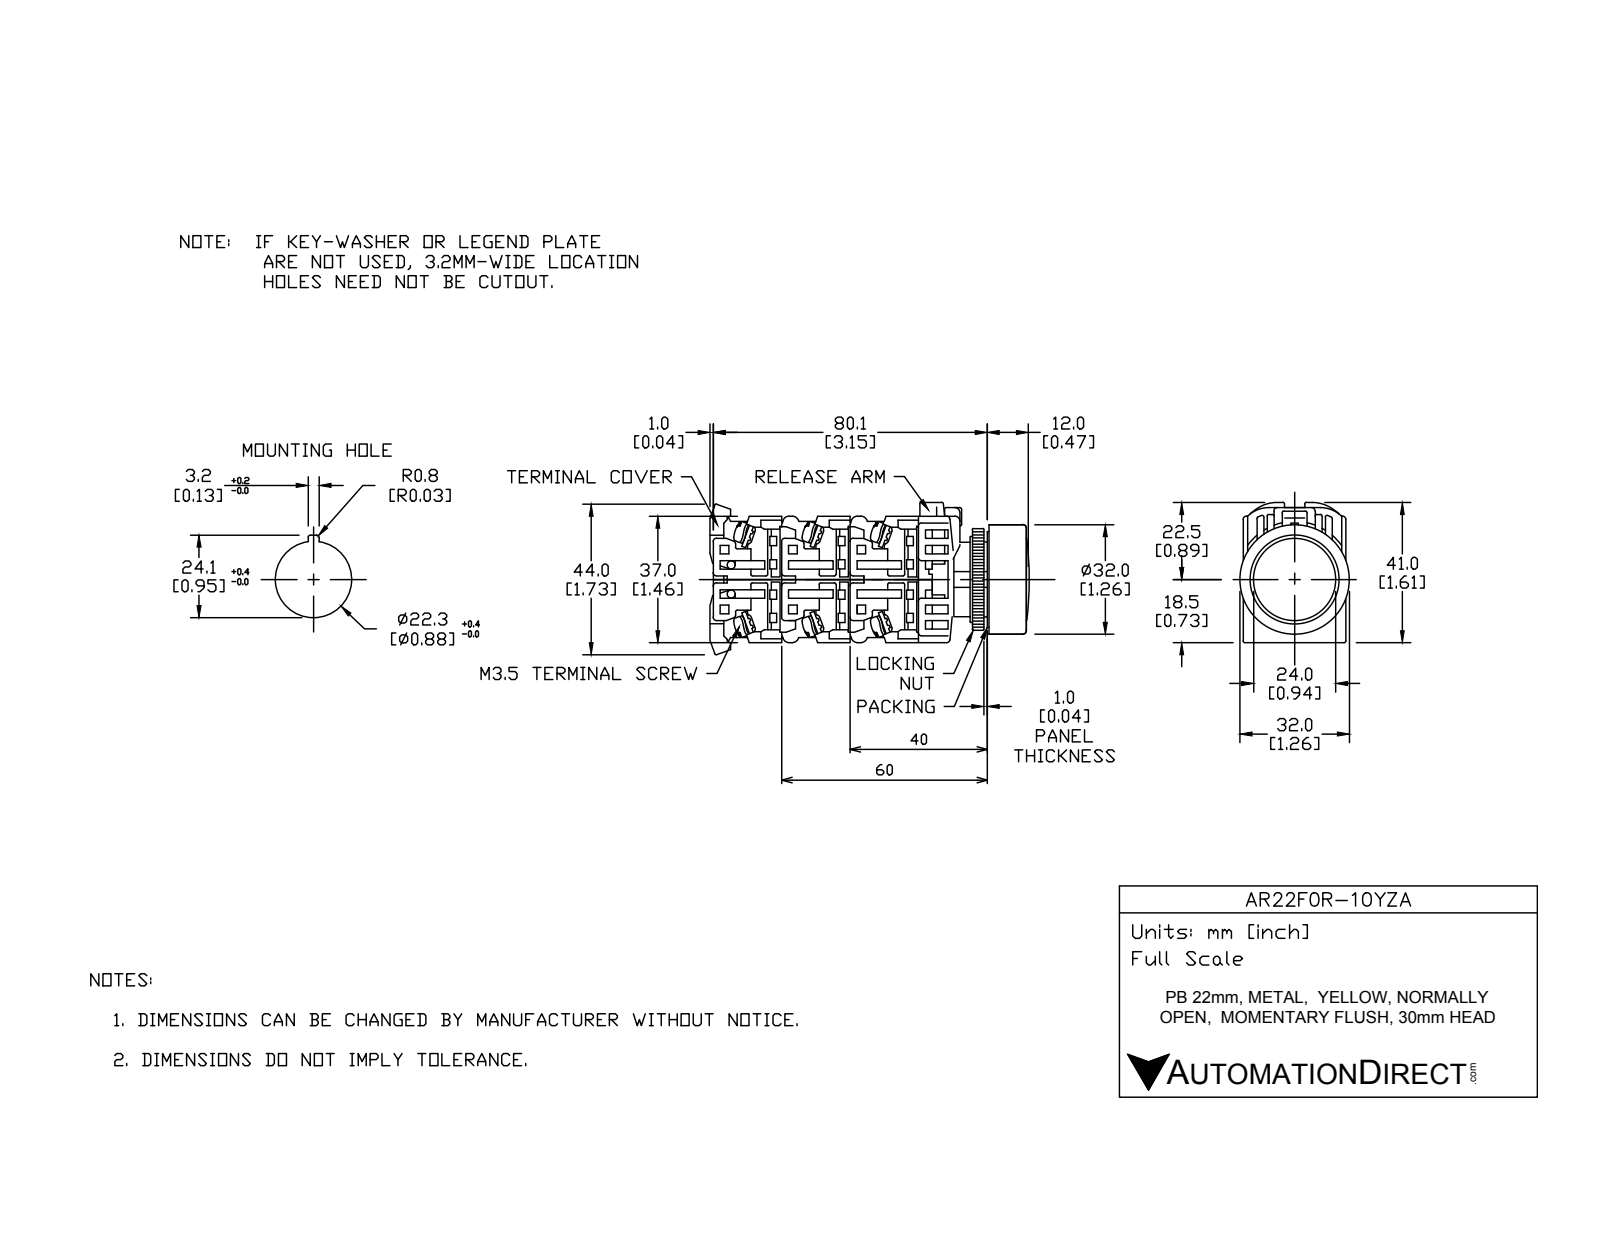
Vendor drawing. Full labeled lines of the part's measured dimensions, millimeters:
Part name (STEP PRODUCT): AR22F0R-10YZA
STEP written by: SolidWorks 2017 (AUTOMOTIVE_DESIGN)
Units: millimetres
Bodies: 12 solids, 295 faces (201 planar, 74 cylindrical, 20 other)
Overall size (bounding box): 52.75 × 41 × 32
Volume: 27 343 mm³ · Surface area: 19 391 mm²
Round holes (diameter × count): ⌀21.8 ×1, ⌀22 ×1, ⌀25 ×1, ⌀31 ×1
Round bosses / shafts (diameter × count): ⌀5 ×2, ⌀32 ×1, ⌀30.5 ×1, ⌀29.8 ×1, ⌀24 ×1, ⌀23.8 ×1, ⌀21.75 ×1, ⌀17 ×1
Partial cylindrical surfaces — rounded edges, fillets, slot ends (radius × count): R0.5 ×23, R1.75 ×4, R5 ×4, R4 ×2, R16.59 ×1, R17.59 ×1
Main face-to-face distances: 1, 28.5, 18, 3, 2, 29, 30, 10.5, 8, 20.5
